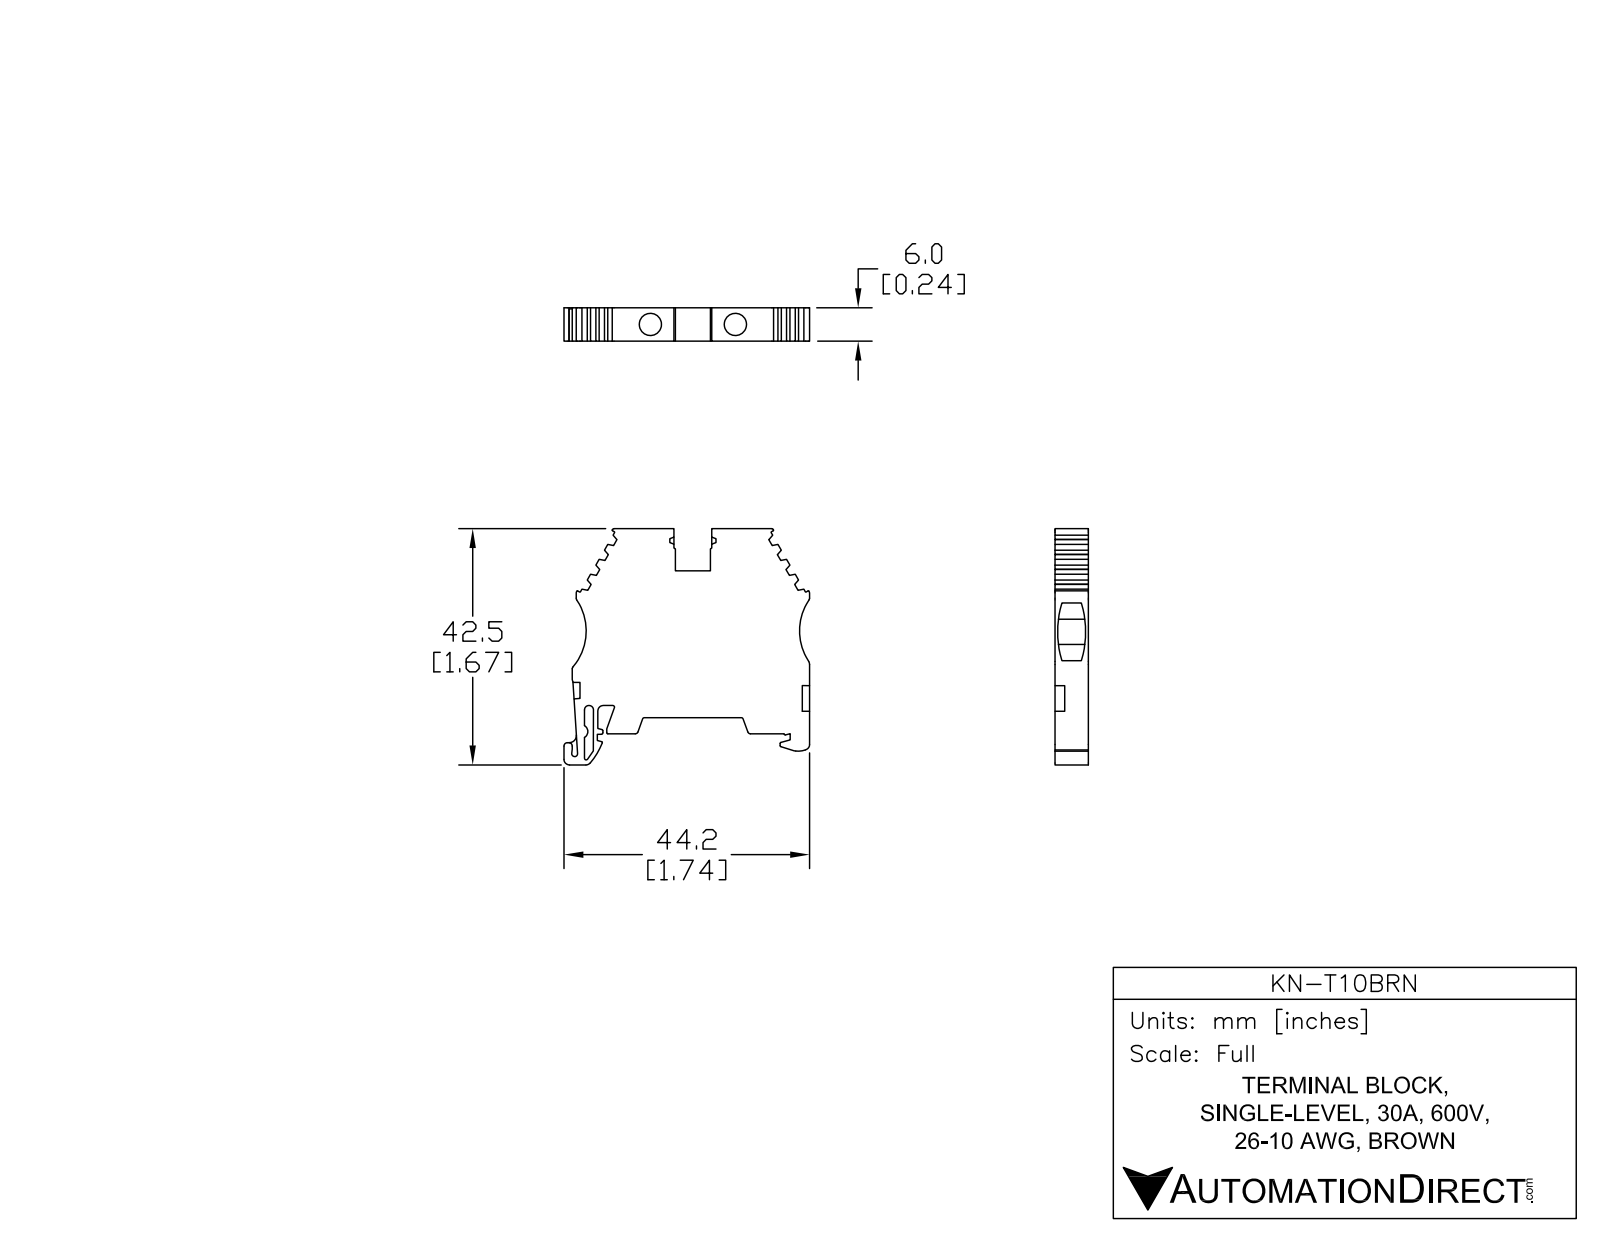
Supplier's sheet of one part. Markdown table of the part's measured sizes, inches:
| quantity | value |
| --- | --- |
| part name | KN-T10 |
| STEP written by | SolidWorks 2014 (AUTOMOTIVE_DESIGN) |
| units | inches |
| bodies | 1 solid, 191 faces (132 planar, 59 cylindrical, 0 other) |
| overall size | 1.74 × 1.673 × 0.236 |
| volume | 0.439 in³ |
| surface area | 7.353 in² |
| round holes (diameter × count) | 0.157 × 2 |
| partial cylindrical surfaces (radius × count) | 0.012 × 10, 0.004 × 8, 0.039 × 6, 0.02 × 4, 0.008 × 3, 0.019 × 2, 0.024 × 2, 0.394 × 2 |
| main face-to-face distances | 0.236, 1.339, 0.114, 1.453, 0.039, 0.115, 0.299, 0.339, 0.587, 0.094 |
| hole center spacings | 0.602 |
